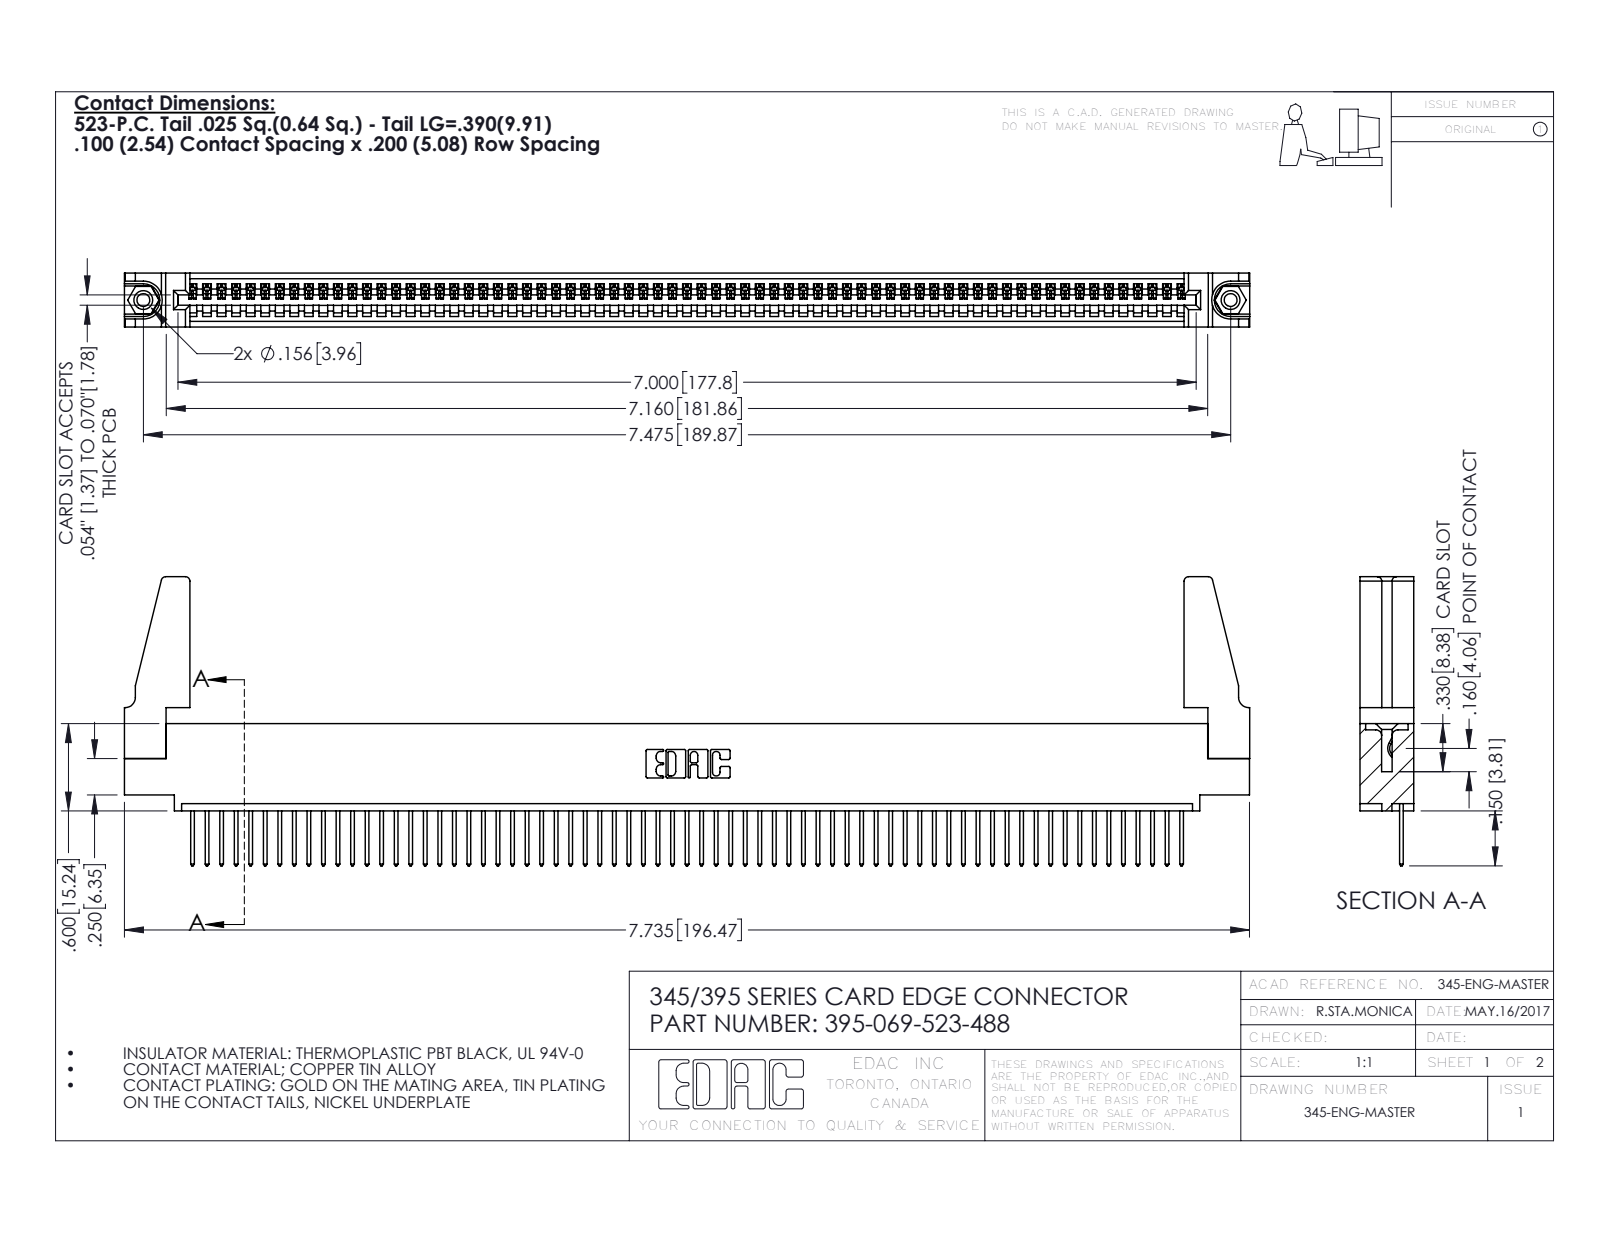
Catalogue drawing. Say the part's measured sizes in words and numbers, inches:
The part is named "345-292-001_345-293-123; 345-220-078_345-220-088; 345-250-001_345-250-001-102; 345 Part_0.110 Offset - 0.156 Dia-TH (+1 more)". Its 3-D file was written by "SolidWorks 2016 (CONFIG_CONTROL_DESIGN)". It is 74 solids with 4256 faces: 2916 planar, 1324 cylindrical and 16 other. Overall it measures 7.736 by 1.987 by 0.37 inches. Its volume is 1.345 cubic inches and its surface area 44.35 square inches. Round holes: 2 of diameter 0.089, 2 of diameter 0.125, 2 of diameter 0.156, 1 of diameter 0.064. Round bosses or shafts: 2 of diameter 0.155. Partial cylindrical surfaces (rounded edges, fillets, slot ends): 138 of radius 0.006, 138 of radius 0.01, 22 of radius 0.01, 8 of radius 0.03, 6 of radius 0.007, 6 of radius 0.031, 3 of radius 0.026, 2 of radius 0.031. The main face-to-face distances are 0.072, 0.298, 0.37, 0.098, 0.272, 0.025, 0.2, 0.225, 0.149, 0.072. The hole center spacings are 0.27, 7.239, 7.475.
